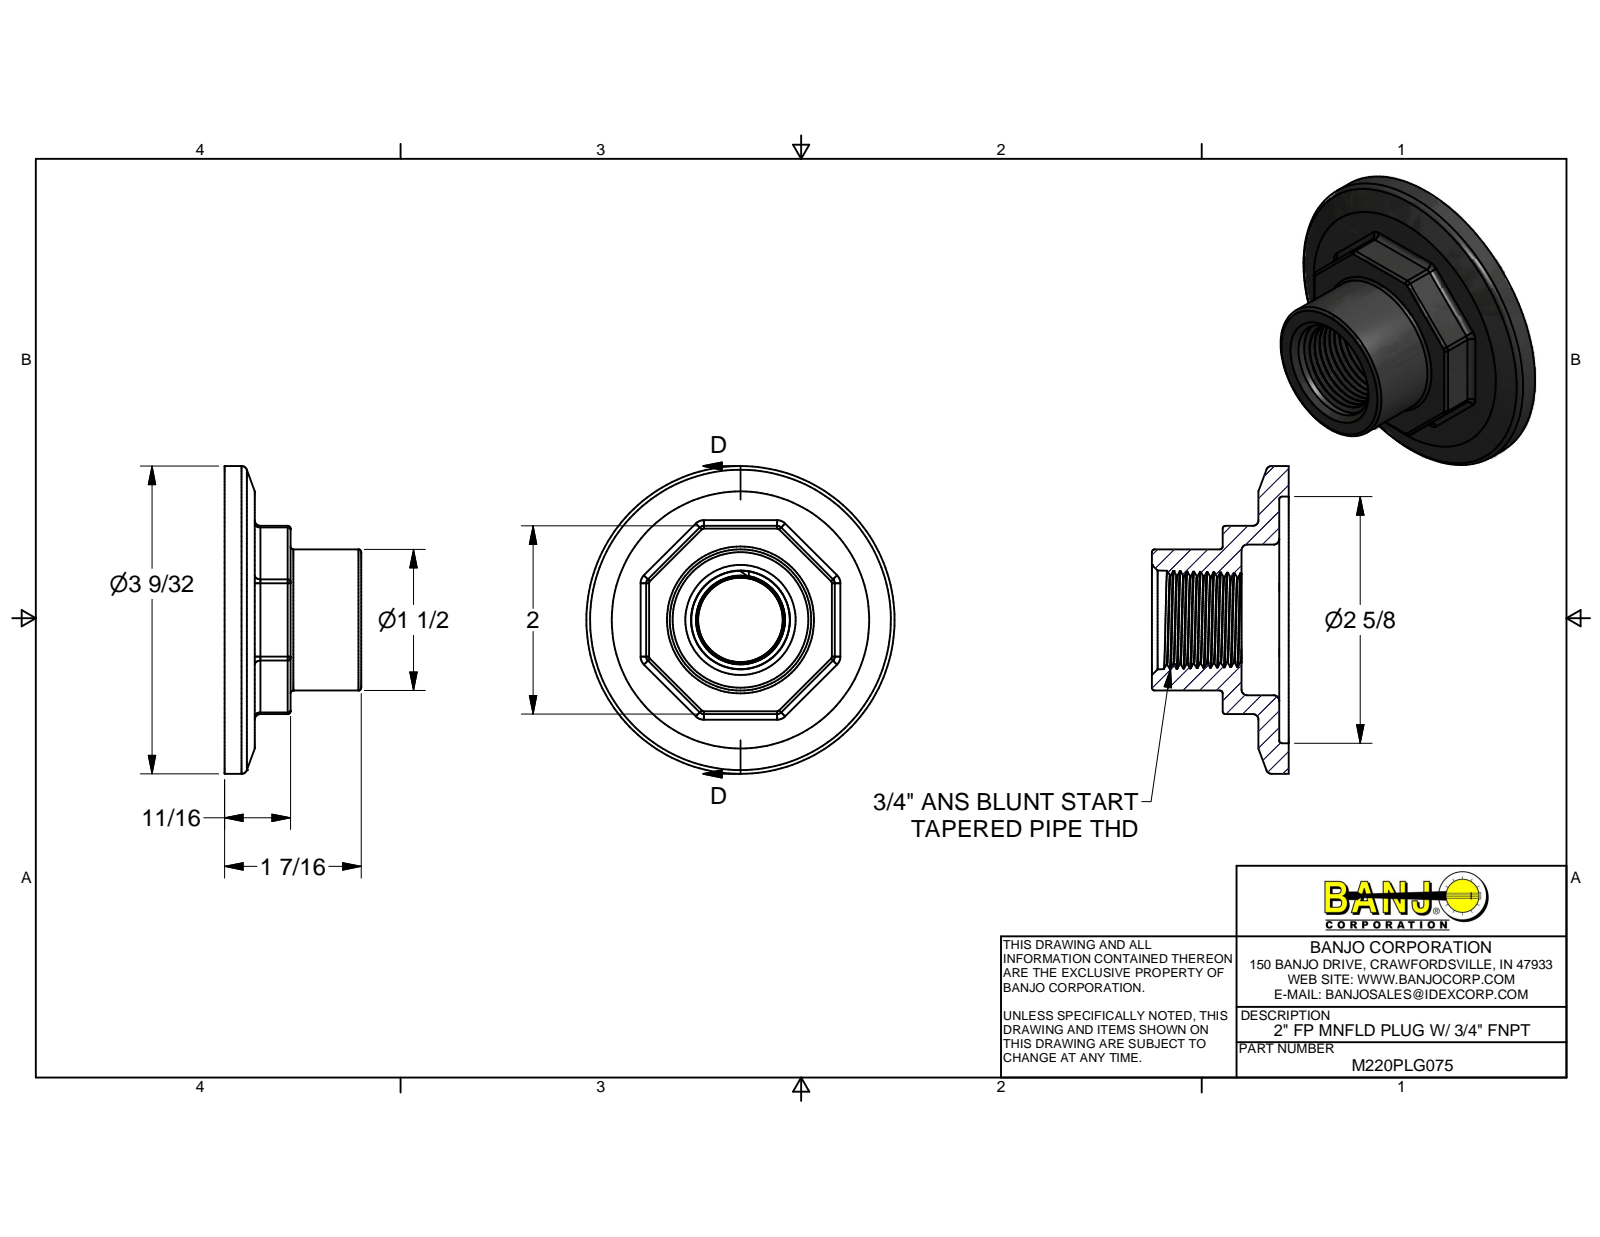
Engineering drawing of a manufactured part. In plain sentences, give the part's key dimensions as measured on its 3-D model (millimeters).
The part is named "M220PLG075". Its 3-D file was written by "Autodesk Inventor 2013 (AUTOMOTIVE_DESIGN)". It is 1 solid with 130 faces: 23 planar, 51 cylindrical and 56 other. Overall it measures 83.1 by 83.1 by 36.8 millimeters. Its volume is 49 670 cubic millimeters and its surface area 19 760 square millimeters. Round holes: 1 of diameter 66.5. Round bosses or shafts: 1 of diameter 83.1, 1 of diameter 38.1. Partial cylindrical surfaces (rounded edges, fillets, slot ends): 40 of radius 1.5, 8 of radius 0.8. The main face-to-face distances are 2.5, 5.1, 8.1, 5.6, 45.7, 17.8, 15.2, 9.7, 12.7, 10.2.
